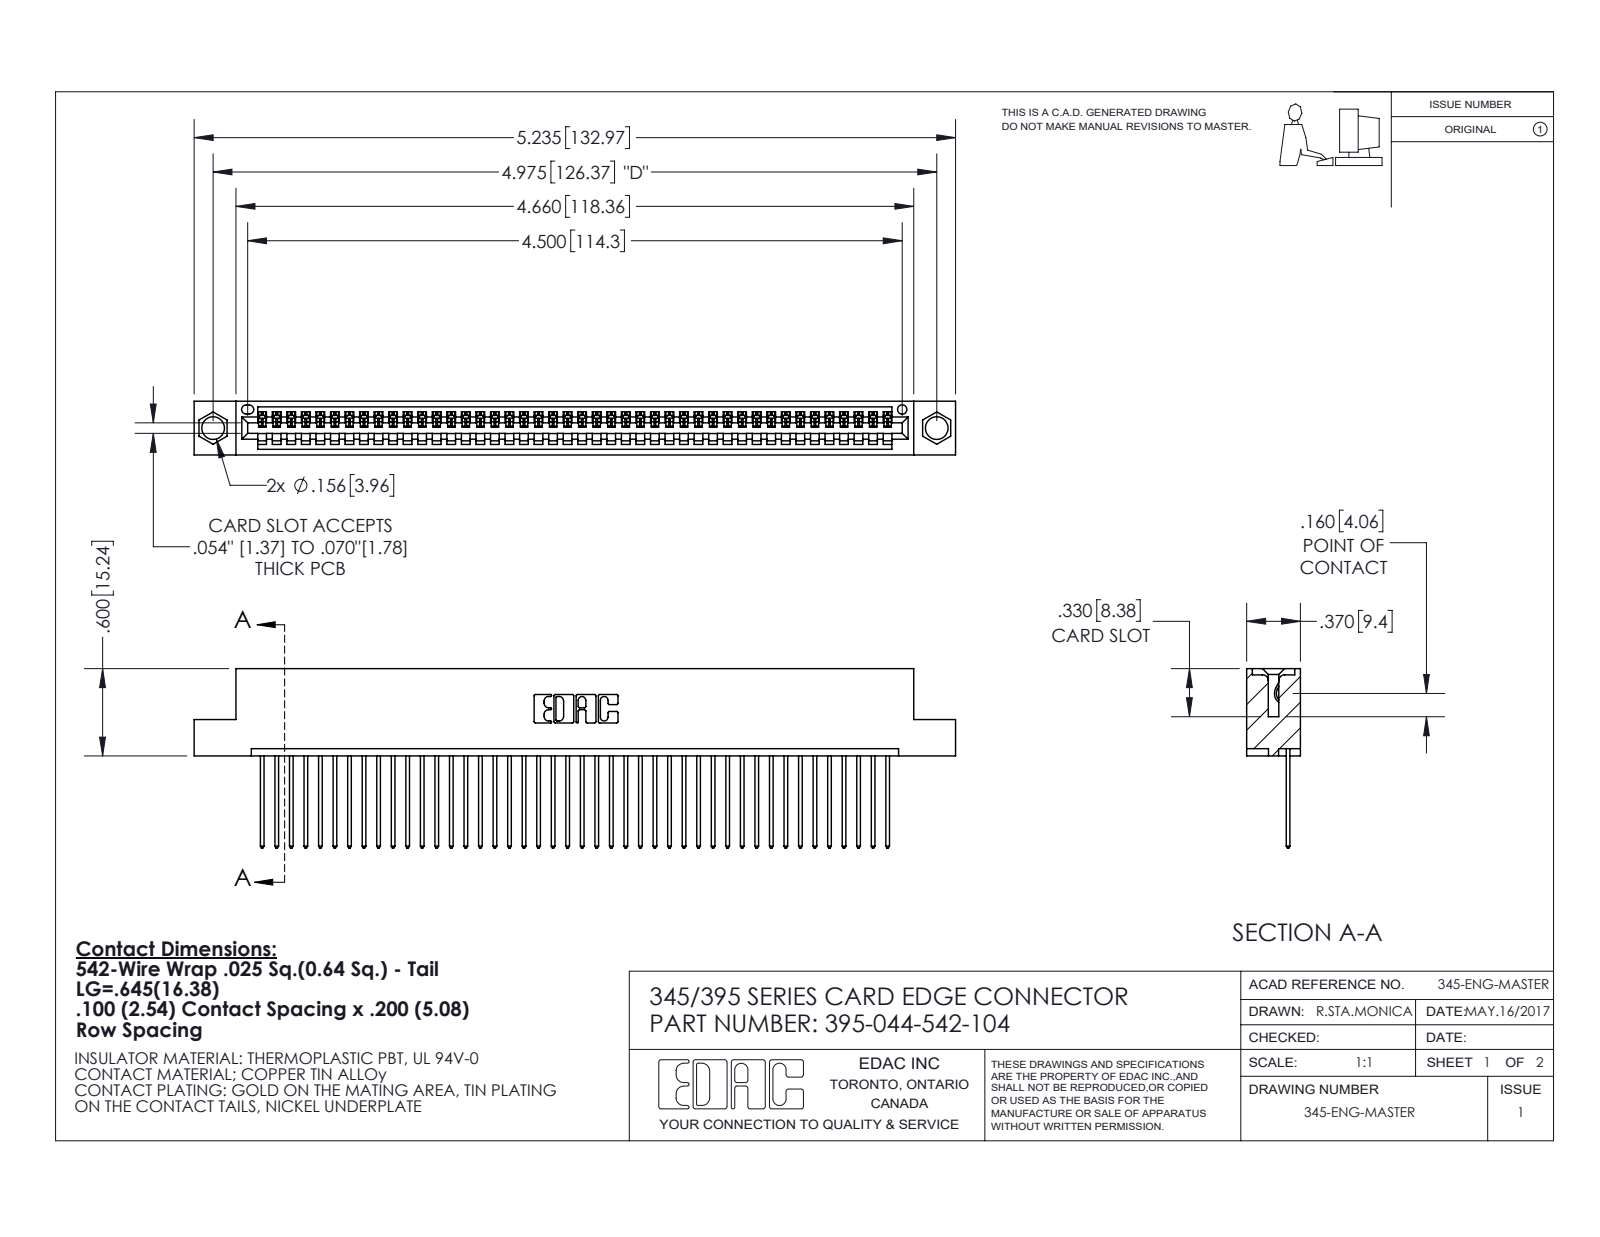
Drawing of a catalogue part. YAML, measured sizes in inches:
part_name: "395-044-542-104; 345 Part_Flush Mounting Lugs - 0.156 Dia-TI; 345-292-001_345-293-142"
step_written_by: "SolidWorks 2020 (CONFIG_CONTROL_DESIGN)"
units: inches
bodies: {solids: 45, faces: 2692, planar: 1854, cylindrical: 838, other: 0}
overall_size: [5.235, 1.232, 0.37]
volume: 0.771
surface_area: 26.79
round_holes:
  - {diameter: 0.156, count: 2}
  - {diameter: 0.064, count: 1}
partial_cylinders:
  - {radius: 0.006, count: 88}
  - {radius: 0.01, count: 88}
  - {radius: 0.01, count: 22}
  - {radius: 0.007, count: 6}
  - {radius: 0.031, count: 6}
  - {radius: 0.026, count: 3}
  - {radius: 0.031, count: 2}
  - {radius: 0.04, count: 2}
face_to_face_distances: [0.072, 0.298, 0.37, 0.098, 0.272, 0.025, 0.2, 0.225, 0.149, 0.072]
hole_center_spacings: [0.27, 4.739, 4.975]
